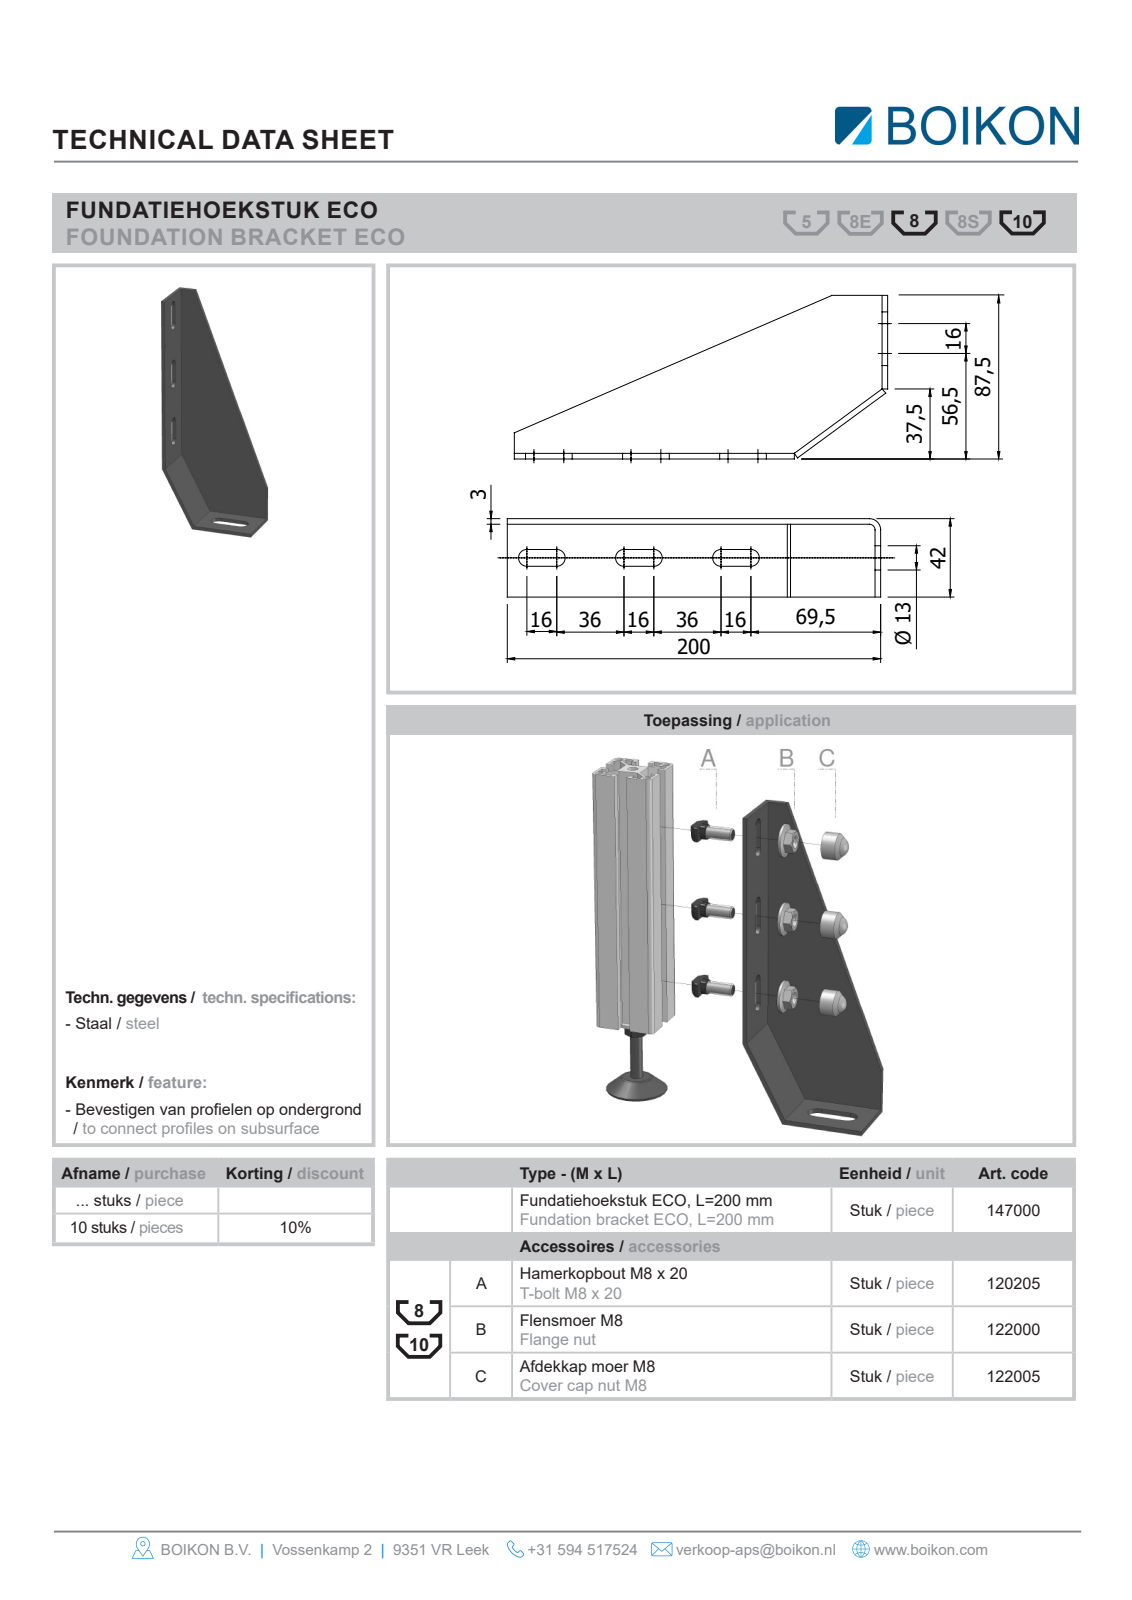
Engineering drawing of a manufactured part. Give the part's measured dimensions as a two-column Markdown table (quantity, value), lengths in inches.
| quantity | value |
| --- | --- |
| part name | Root; 147000Fundatie-hoekstuk, Eco, L=200BOIKON |
| STEP written by | HiCAD 2013 1802.4 Build 509 (AUTOMOTIVE_DESIGN) |
| units | inches |
| bodies | 1 solid, 28 faces (20 planar, 8 cylindrical, 0 other) |
| overall size | 7.913 × 4.035 × 1.654 |
| volume | 4.01 in³ |
| surface area | 62.35 in² |
| partial cylindrical surfaces (radius × count) | 0.177 × 6, 0.256 × 2 |
| main face-to-face distances | 0.157, 0.118, 1.496, 1.654, 3.031, 3.15, 7.913, 7.795, 0.591, 0.945 |
